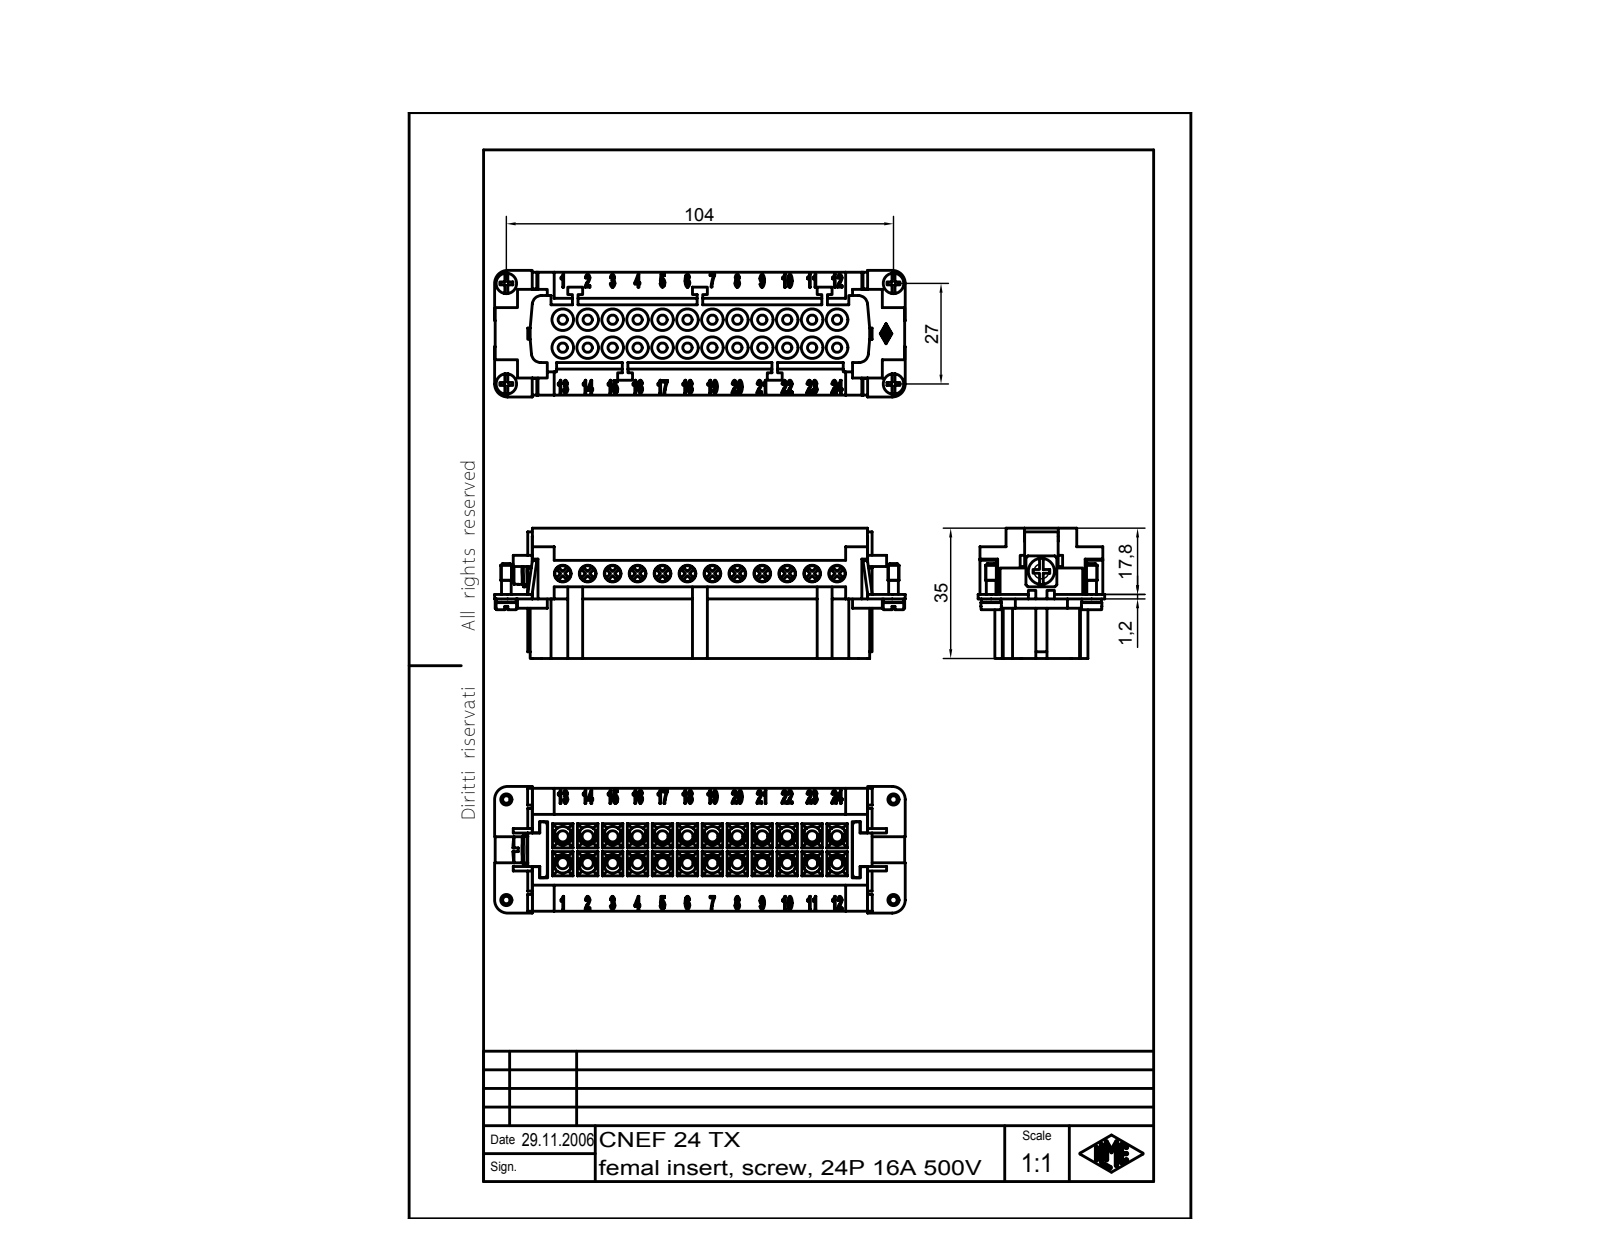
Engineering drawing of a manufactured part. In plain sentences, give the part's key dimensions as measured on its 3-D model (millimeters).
The part is named "CNEF 24 TX". Its 3-D file was written by "Autodesk Inventor 7 (AUTOMOTIVE_DESIGN)". It is 1 solid with 2425 faces: 1044 planar, 182 cylindrical and 1199 other. Overall it measures 110.3 by 35 by 34 millimeters. Its volume is 57 336 cubic millimeters and its surface area 39 009 square millimeters. Round holes: 12 of diameter 3, 12 of diameter 4.5, 12 of diameter 5, 1 of diameter 3.24. Round bosses or shafts: 12 of diameter 4.2, 2 of diameter 5.5, 2 of diameter 5.3, 2 of diameter 3, 2 of diameter 2.6, 1 of diameter 7. Partial cylindrical surfaces (rounded edges, fillets, slot ends): 14 of radius 0.1, 12 of radius 2.1, 4 of radius 2.5, 2 of radius 1, 2 of radius 3.5, 1 of radius 5.5. The main face-to-face distances are 1.75, 17.25, 19, 15.5, 24.25, 7.1, 7, 8.75, 26, 3.25. The hole center spacings are 6.7, 13.4, 20.1, 26.8, 33.5, 40.2, 46.9, 53.6.
